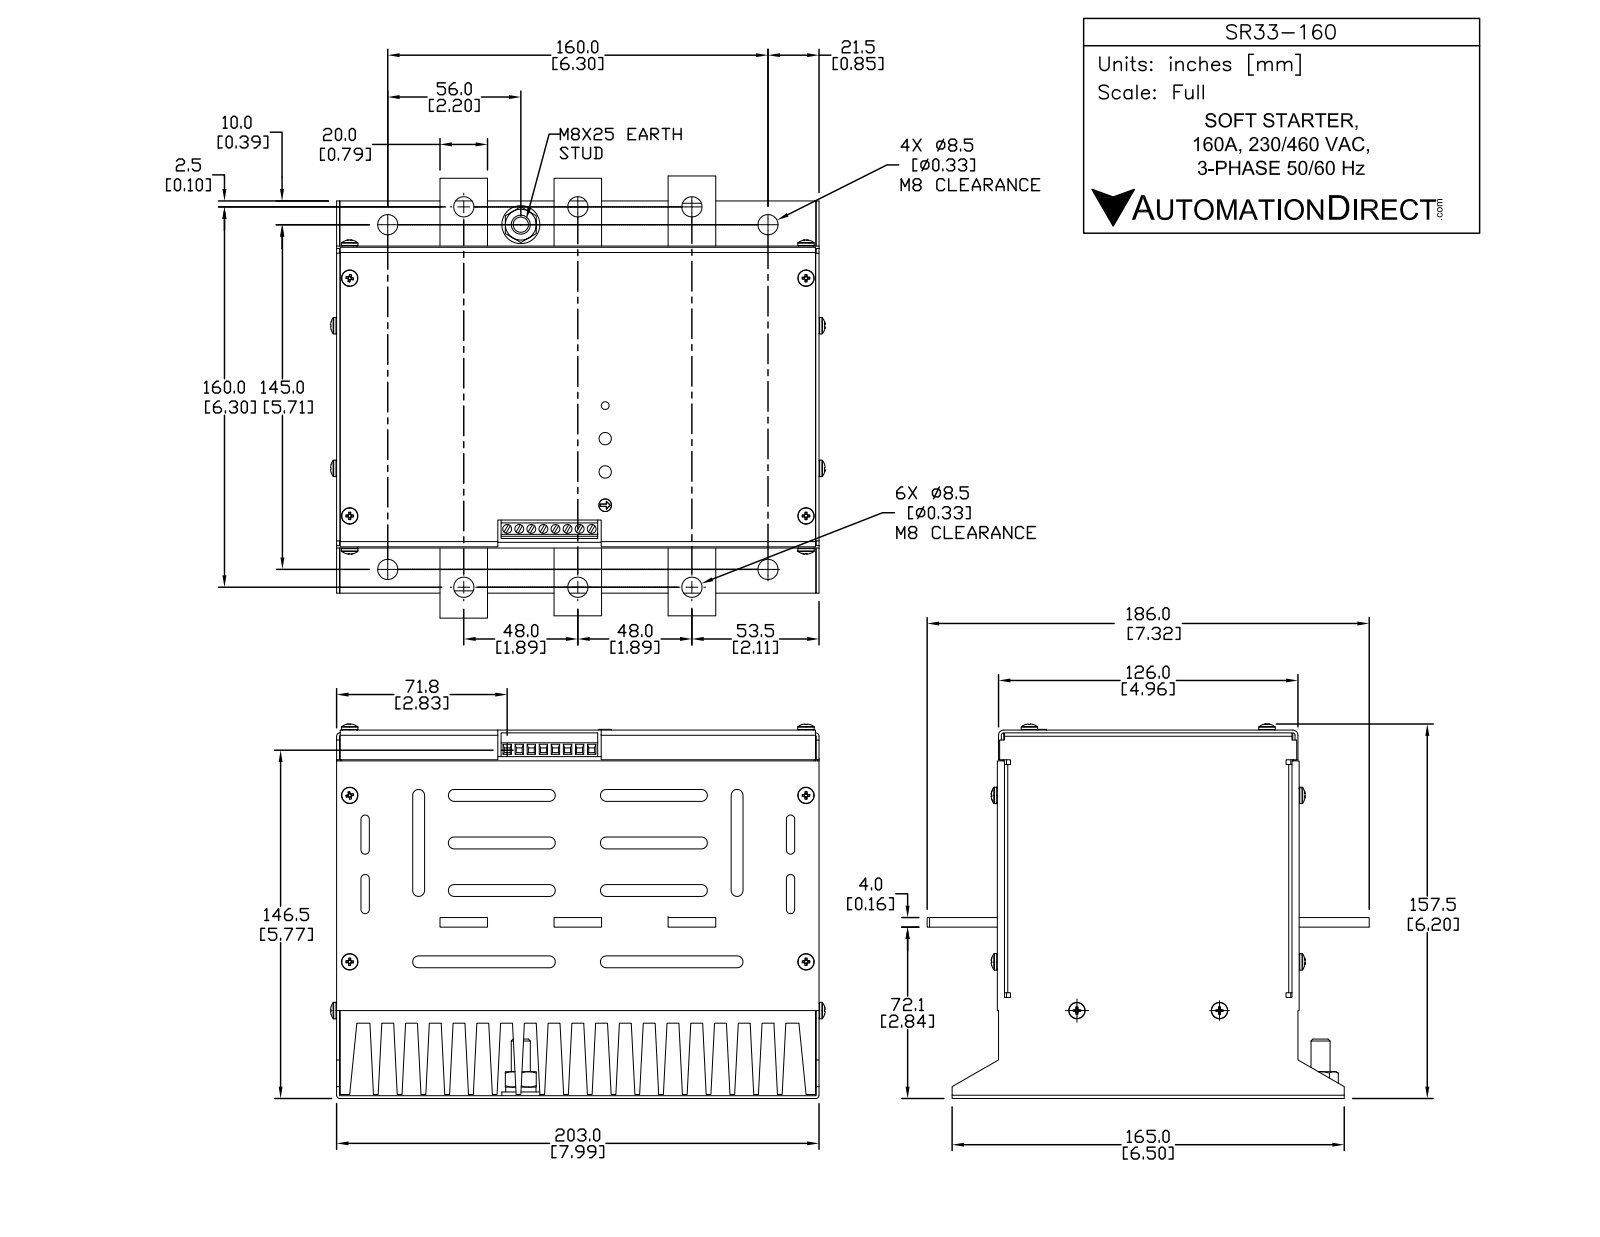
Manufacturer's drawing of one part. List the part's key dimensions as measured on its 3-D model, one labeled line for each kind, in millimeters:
Part name (STEP PRODUCT): SR33-160
STEP written by: SolidWorks 2013 (AUTOMOTIVE_DESIGN)
Units: millimetres
Bodies: 1 solid, 881 faces (580 planar, 155 cylindrical, 146 other)
Overall size (bounding box): 203 × 186 × 158
Volume: 3 204 000 mm³ · Surface area: 529 358 mm²
Round holes (diameter × count): ⌀3.82 ×8, ⌀8.5 ×4
Round bosses / shafts (diameter × count): ⌀6.9 ×8, ⌀16 ×7, ⌀8.5 ×6, ⌀8 ×1
Partial cylindrical surfaces — rounded edges, fillets, slot ends (radius × count): R2.5 ×20, R1.75 ×8, R1 ×4, R2 ×2
Main face-to-face distances: 9.99, 19.98, 29.97, 39.96, 49.95, 59.94, 69.93, 79.92, 89.91, 99.9
Hole centre spacings: 4.92, 9.84, 14.76, 19.68, 24.6, 29.52, 145, 160
